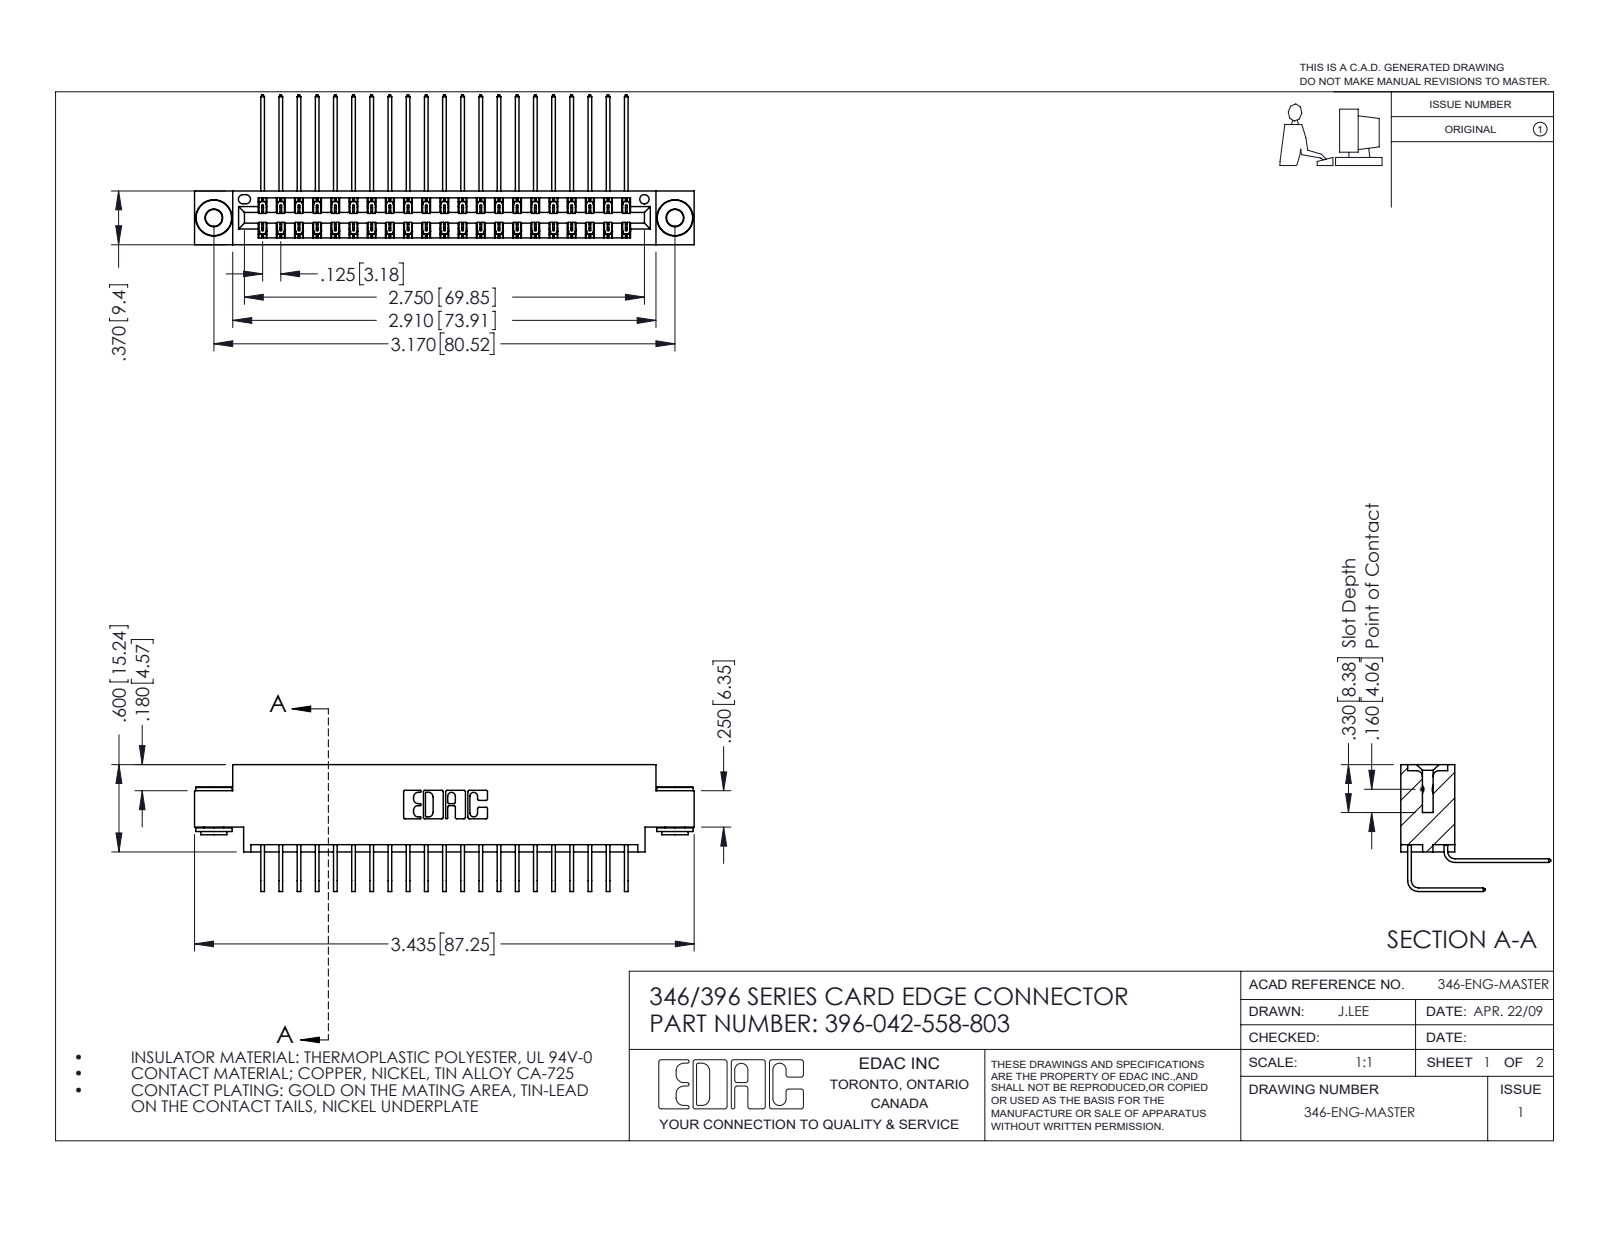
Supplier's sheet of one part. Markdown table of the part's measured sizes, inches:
| quantity | value |
| --- | --- |
| part name | 396-042-558-803; 345-292-001_558 559 Tail - 1; 345-292-001_558 Tail - 2; 345-250-002_345-250-002-102 (+1 more) |
| STEP written by | SolidWorks 2016 (CONFIG_CONTROL_DESIGN) |
| units | inches |
| bodies | 45 solids, 2432 faces (1644 planar, 780 cylindrical, 8 other) |
| overall size | 3.435 × 1.03 × 0.873 |
| volume | 0.516 in³ |
| surface area | 19.91 in² |
| round holes (diameter × count) | 0.116 × 2, 0.156 × 2, 0.064 × 1 |
| round bosses / shafts (diameter × count) | 0.25 × 2, 0.18 × 2, 0.136 × 2 |
| partial cylindrical surfaces (radius × count) | 0.006 × 63, 0.01 × 22, 0.007 × 6, 0.031 × 6, 0.026 × 3, 0.014 × 2, 0.022 × 2, 0.024 × 2 |
| main face-to-face distances | 0.322, 0.048, 0.025, 0.37, 0.25, 0.298, 0.072, 0.275, 0.148, 0.222 |
| hole center spacings | 0.246, 2.963, 3.17 |
